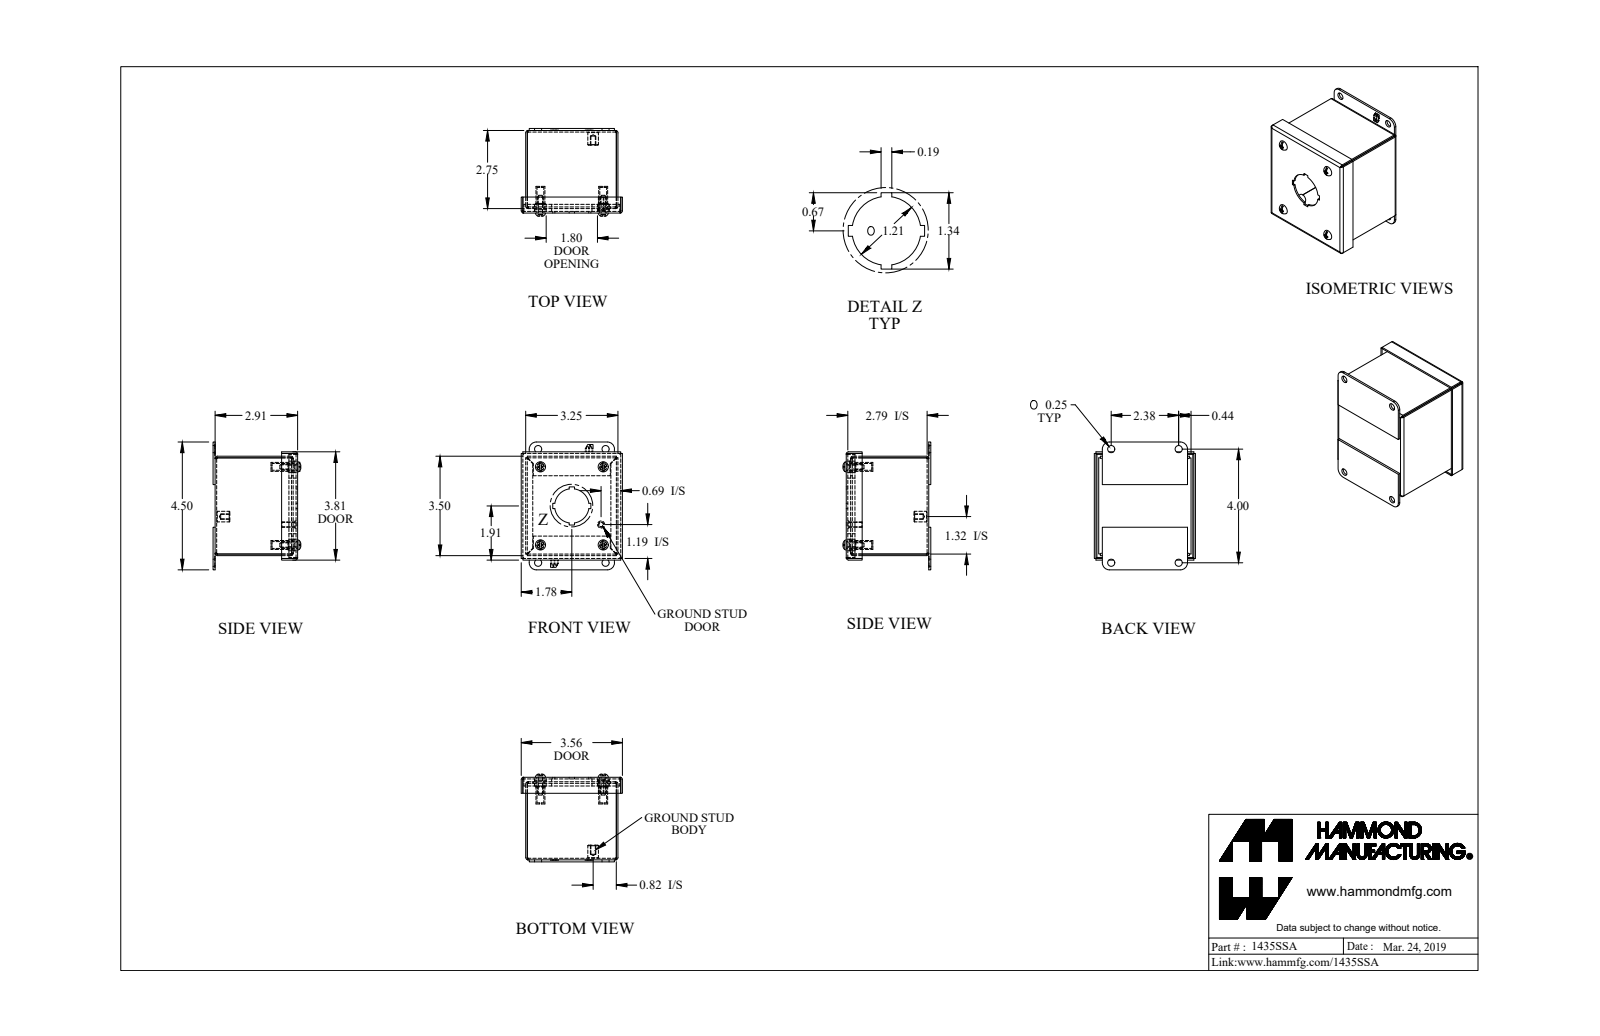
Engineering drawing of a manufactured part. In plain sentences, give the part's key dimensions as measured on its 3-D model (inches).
The part is named "1435SSA_Default". Its 3-D file was written by "SolidWorks 2019 (CONFIG_CONTROL_DESIGN)". It is 19 solids with 461 faces: 295 planar, 136 cylindrical and 30 other. Overall it measures 4.5 by 3.562 by 3.089 inches. Its volume is 6.173 cubic inches and its surface area 190.7 square inches. Round holes: 8 of diameter 0.25, 4 of diameter 0.065, 4 of diameter 0.239, 4 of diameter 0.253, 4 of diameter 0.406, 1 of diameter 0.156, 1 of diameter 1.21. Round bosses or shafts: 5 of diameter 0.19, 4 of diameter 0.406, 4 of diameter 0.315, 4 of diameter 0.148, 1 of diameter 0.375, 1 of diameter 0.25. Partial cylindrical surfaces (rounded edges, fillets, slot ends): 12 of radius 0.029, 12 of radius 0.086, 4 of radius 0.171, 4 of radius 0.25, 2 of radius 0.125. The main face-to-face distances are 0.057, 2.85, 0.057, 3.193, 3.443, 2.907, 2.793, 0.156, 2.979, 2.922. The hole center spacings are 2.211, 2.75, 0.63, 2.212, 2.75, 3.376, 3.529, 4.08.
